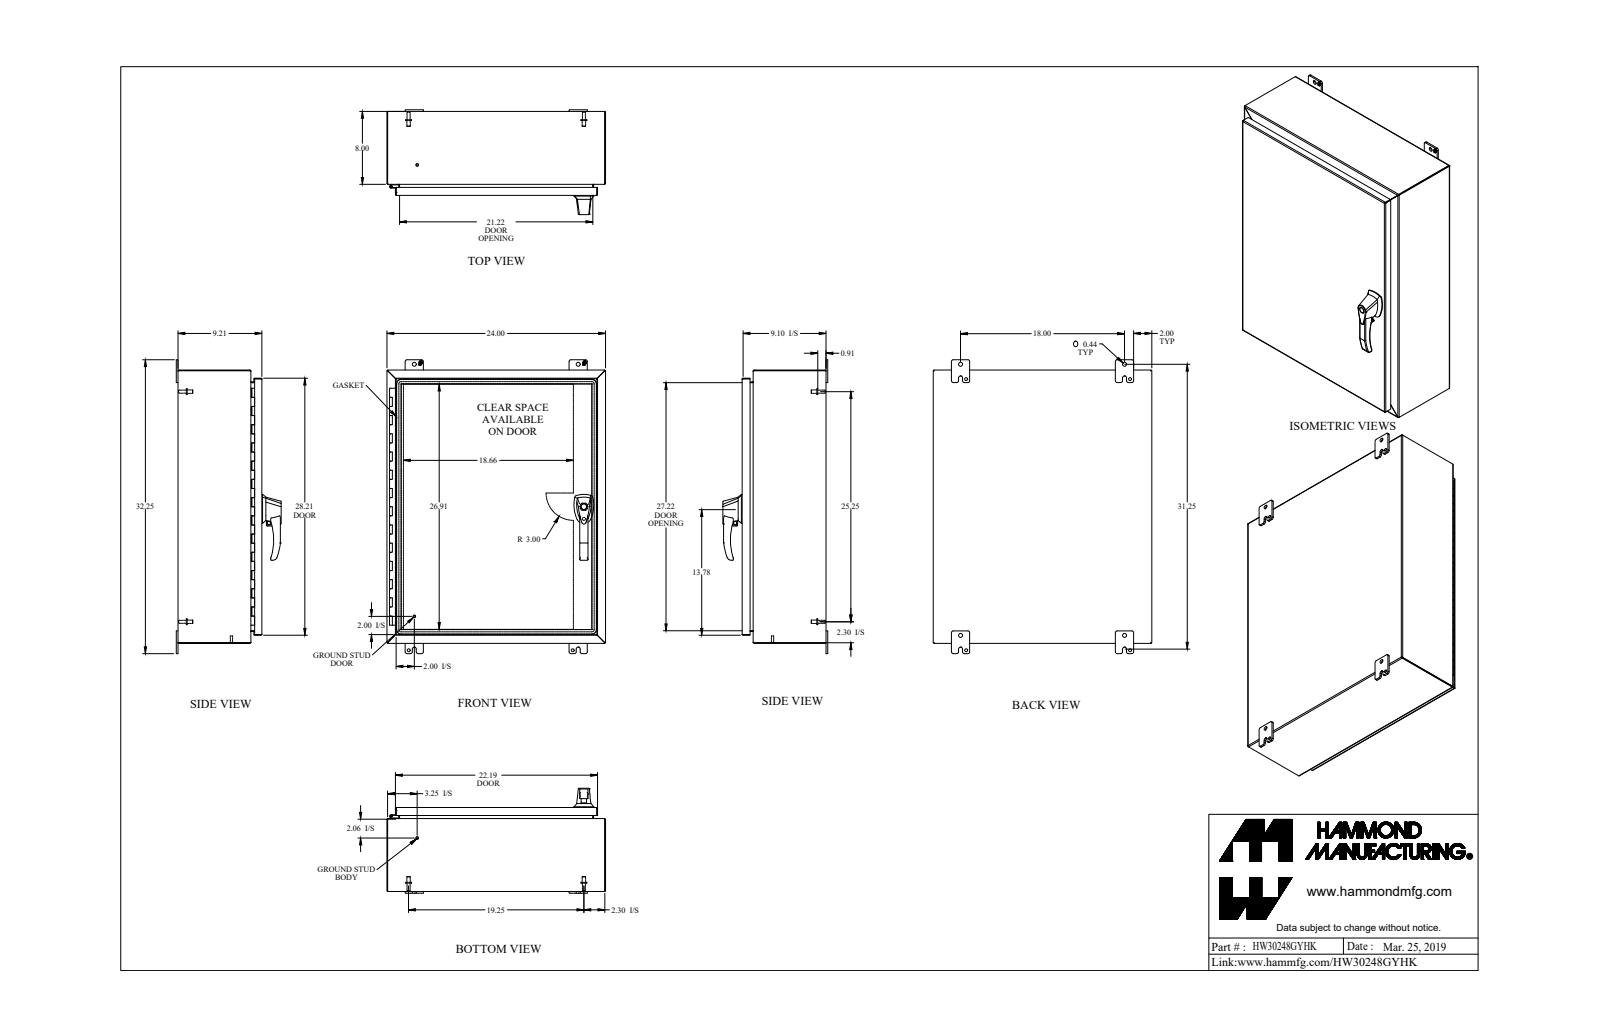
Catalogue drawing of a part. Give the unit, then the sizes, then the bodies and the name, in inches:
Units: inches
Overall size (bounding box): 32.25 × 24 × 11.512
Round holes (diameter × count): ⌀0.176 ×6, ⌀0.313 ×4, ⌀0.25 ×3, ⌀0.265 ×3, ⌀0.413 ×3, ⌀0.196 ×2, ⌀0.256 ×2, ⌀0.394 ×2, ⌀0.437 ×2, ⌀0.187 ×1, ⌀0.233 ×1, ⌀0.334 ×1
Round bosses / shafts (diameter × count): ⌀0.375 ×9, ⌀0.25 ×7, ⌀0.156 ×6, ⌀0.65 ×4, ⌀0.33 ×4, ⌀1 ×3, ⌀0.63 ×2, ⌀0.51 ×2
Partial cylindrical surfaces — rounded edges, fillets, slot ends (radius × count): R0.25 ×27, R0.188 ×24, R0.036 ×20, R0.108 ×20, R0.06 ×12, R0.125 ×9, R0.045 ×8, R0.218 ×8
Main face-to-face distances: 0.072, 0.072, 9.138, 9.066, 9.21, 9.138, 23.928, 29.928, 7.928, 23.856
Hole centre spacings: 11.118, 11.119, 22.237, 1.111, 11.119, 18, 31.381, 1.005
Volume: 221.5 in³ · Surface area: 5 701 in²
Bodies: 39 solids, 1419 faces (692 planar, 583 cylindrical, 144 other)
Part name (STEP PRODUCT): HW30248GYHK
STEP written by: SolidWorks 2018 (AUTOMOTIVE_DESIGN)
